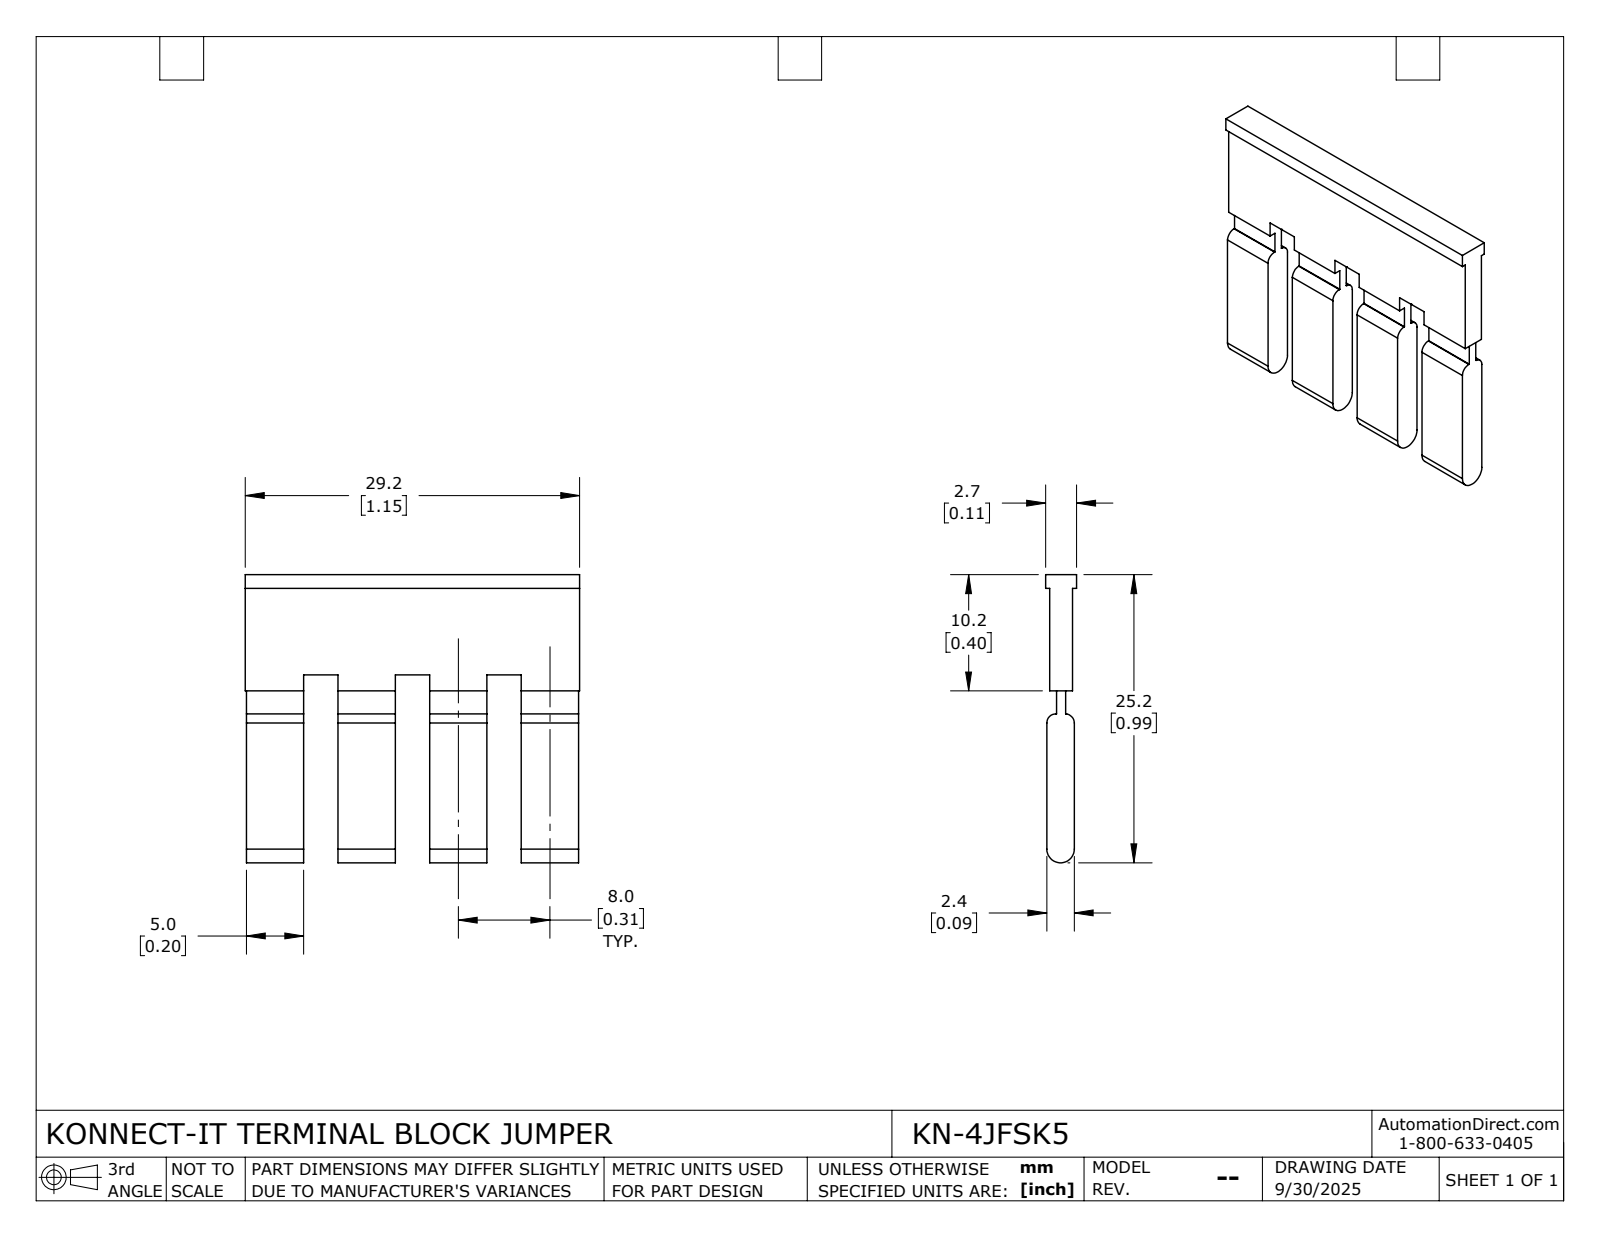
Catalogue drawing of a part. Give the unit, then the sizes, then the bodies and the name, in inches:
Units: inches
Overall size (bounding box): 1.15 × 0.99 × 0.106
Partial cylindrical surfaces — rounded edges, fillets, slot ends (radius × count): R0.031 ×3, R0.047 ×1
Main face-to-face distances: 0.079, 0.089, 0.085, 0.094, 0.315, 0.63, 0.197, 0.118, 0.512, 0.055
Volume: 0.075 in³ · Surface area: 2.587 in²
Bodies: 1 solid, 62 faces (46 planar, 16 cylindrical, 0 other)
Part name (STEP PRODUCT): KN-4JFSK5
STEP written by: SolidWorks 2024 (CONFIG_CONTROL_DESIGN)
